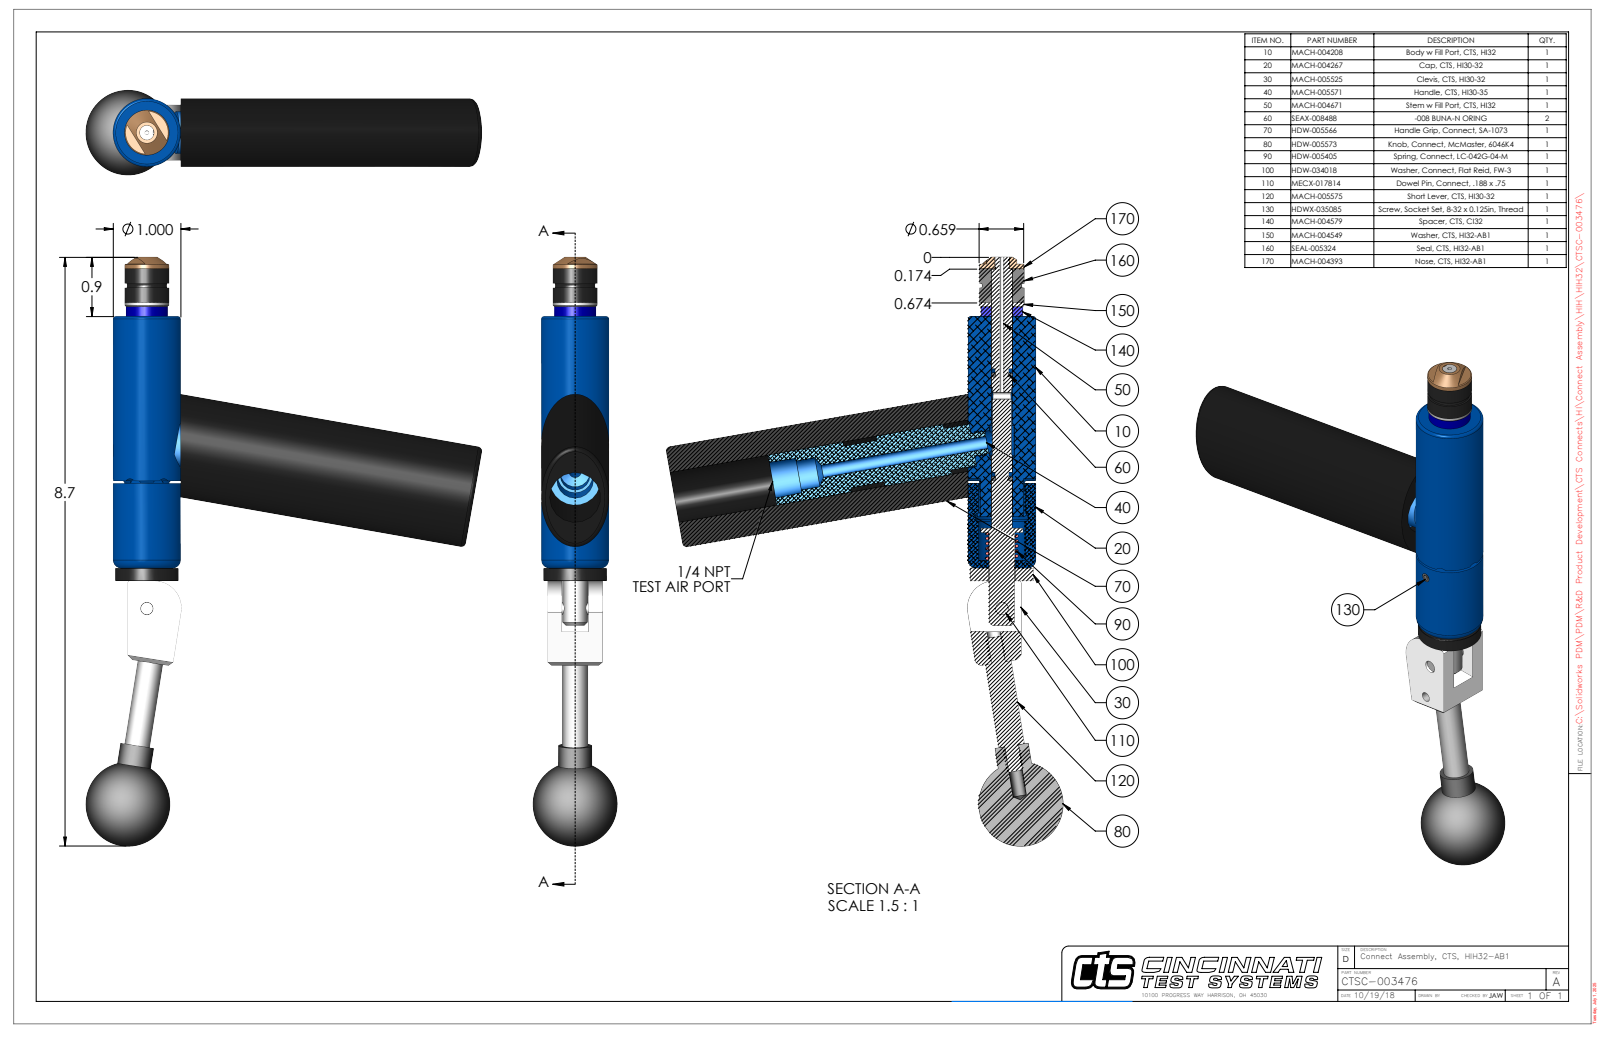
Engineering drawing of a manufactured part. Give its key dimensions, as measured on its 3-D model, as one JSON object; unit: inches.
{"part_name": "CTSC-003476", "step_written_by": "SolidWorks 2023 (AUTOMOTIVE_DESIGN)", "units": "inches", "bodies": {"solids": 11, "faces": 303, "planar": 107, "cylindrical": 126, "other": 70}, "overall_size": [8.704, 5.856, 1.25], "volume_in3": 9.321, "surface_area_in2": 77.46, "round_holes": [[0.201, 2], [0.063, 1], [0.109, 1], [0.136, 1], [0.15, 1], [0.187, 1], [0.189, 1], [0.213, 1], [0.31, 1], [0.314, 1], [0.316, 1], [0.385, 1]], "round_bosses_or_shafts": [[0.25, 2], [0.201, 2], [1, 1], [0.936, 1], [0.75, 1], [0.659, 1], [0.62, 1], [0.618, 1]], "partial_cylinders_radius": [[0.093, 6], [0.029, 2], [0.066, 1], [0.325, 1], [0.4, 1], [0.451, 1]], "face_to_face_distances": [0.21, 0.602, 3.719, 0.812, 3.906, 0.187, 0.702, 4.42, 4.608, 0.785], "hole_center_spacings": [0.599, 1.658, 2.252]}
